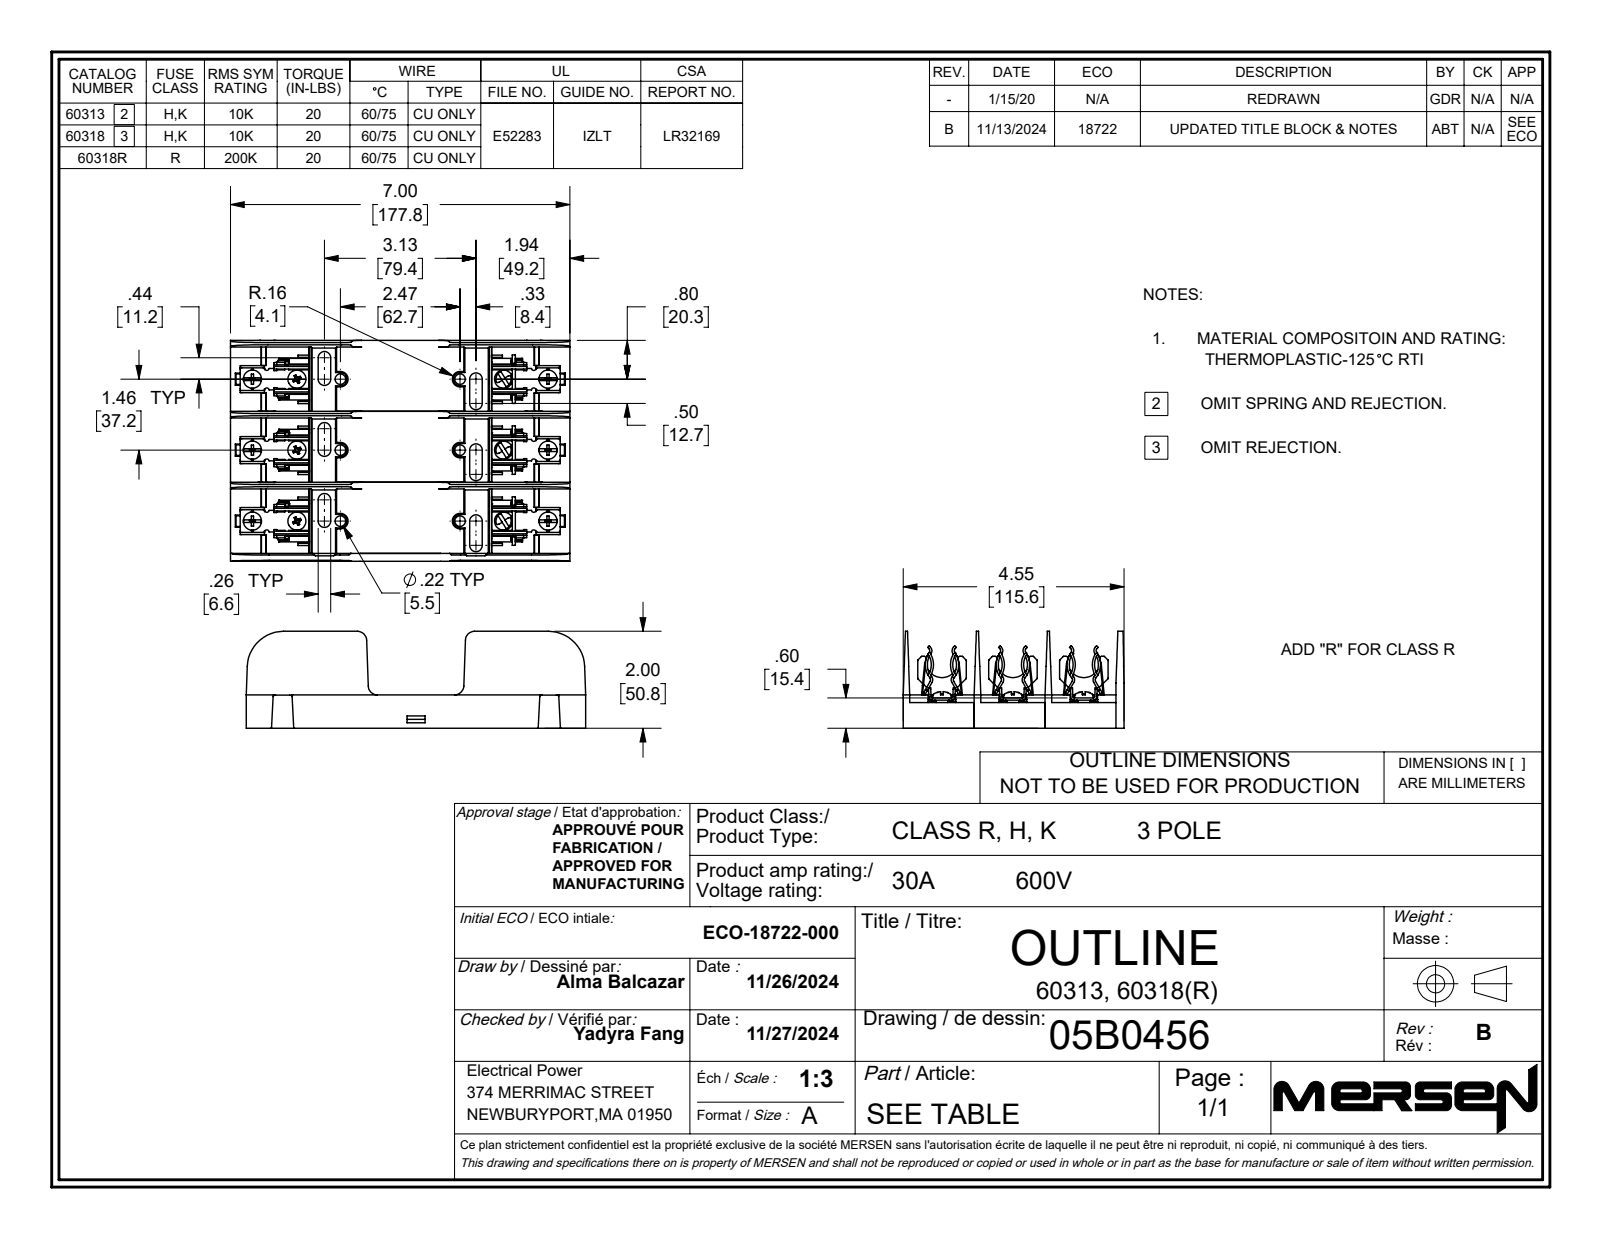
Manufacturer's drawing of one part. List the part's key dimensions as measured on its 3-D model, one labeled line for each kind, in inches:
Part name (STEP PRODUCT): U09360; U00038; U09361; F08907 (+7 more)
STEP written by: SolidWorks 2021 (AUTOMOTIVE_DESIGN)
Units: inches
Bodies: 37 solids, 3451 faces (1693 planar, 1044 cylindrical, 714 other)
Overall size (bounding box): 7 × 4.553 × 2
Volume: 12.56 in³ · Surface area: 279.2 in²
Round holes (diameter × count): ⌀0.159 ×6, ⌀0.218 ×6
Round bosses / shafts (diameter × count): ⌀0.374 ×6, ⌀0.373 ×6, ⌀0.239 ×6, ⌀0.19 ×6, ⌀0.156 ×6, ⌀0.115 ×3
Partial cylindrical surfaces — rounded edges, fillets, slot ends (radius × count): R0.01 ×46, R0.02 ×38, R0.004 ×36, R0.015 ×30, R0.032 ×24, R0.05 ×18, R0.025 ×12, R0.04 ×12
Main face-to-face distances: 1.461, 1.463, 2.923, 1.462, 2.926, 0.53, 0.69, 0.16, 0.02, 0.04
Hole centre spacings: 1.463, 2.331, 4.525, 1.815, 4.282, 2.869, 2.926, 3.443
